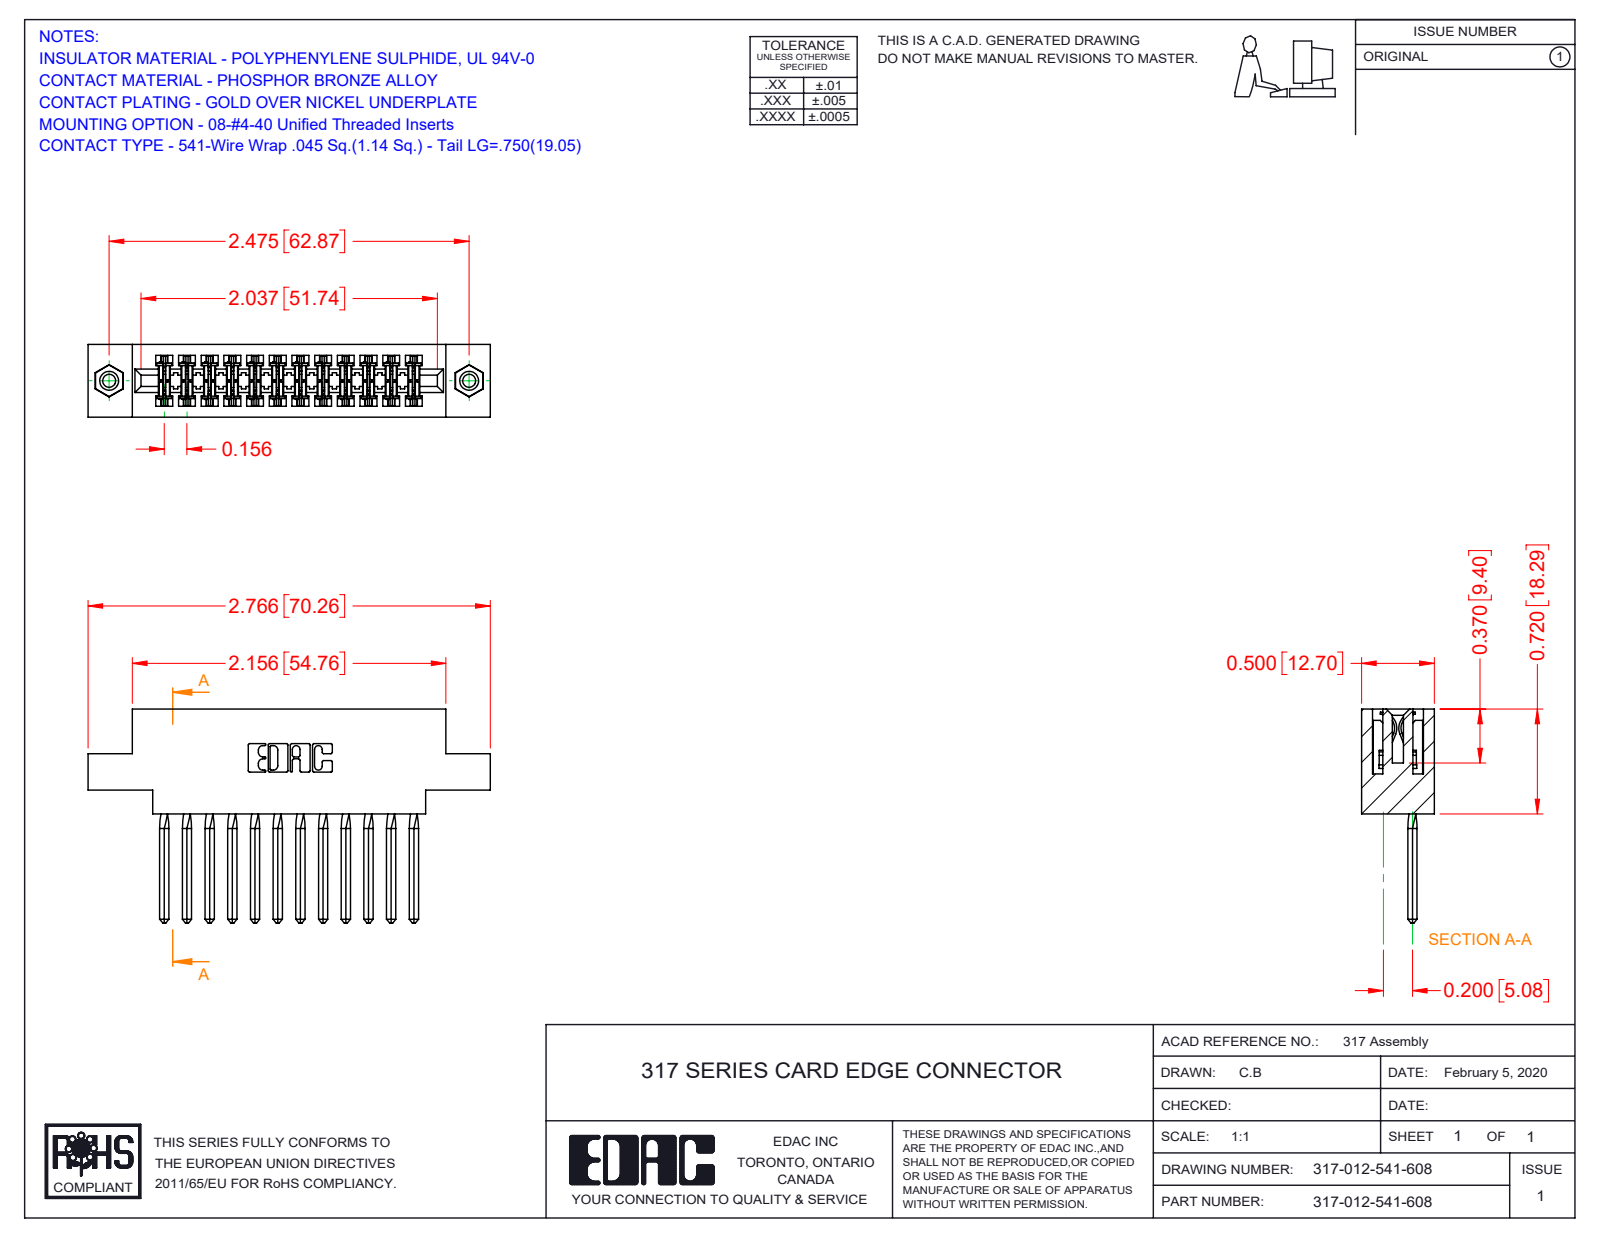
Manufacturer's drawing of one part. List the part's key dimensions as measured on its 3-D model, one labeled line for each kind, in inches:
Part name (STEP PRODUCT): 317-012-541-678; 317 Part_.156 Dia - TI; 345-250-001_345-250-003-102; 317-290-002_541
STEP written by: SolidWorks 2016 (CONFIG_CONTROL_DESIGN)
Units: inches
Bodies: 15 solids, 1986 faces (1578 planar, 344 cylindrical, 64 other)
Overall size (bounding box): 2.766 × 1.47 × 0.5
Volume: 0.639 in³ · Surface area: 21.4 in²
Round holes (diameter × count): ⌀0.089 ×2, ⌀0.125 ×2, ⌀0.156 ×2
Round bosses / shafts (diameter × count): ⌀0.155 ×2
Partial cylindrical surfaces — rounded edges, fillets, slot ends (radius × count): R0.015 ×24, R0.01 ×22, R0.007 ×6, R0.031 ×6, R0.026 ×3, R0.095 ×2, R0.1 ×2, R0.11 ×2
Main face-to-face distances: 0.5, 0.075, 0.425, 0.11, 0.22, 0.065, 0.35, 0.331, 0.195, 0.136
Hole centre spacings: 2.475
